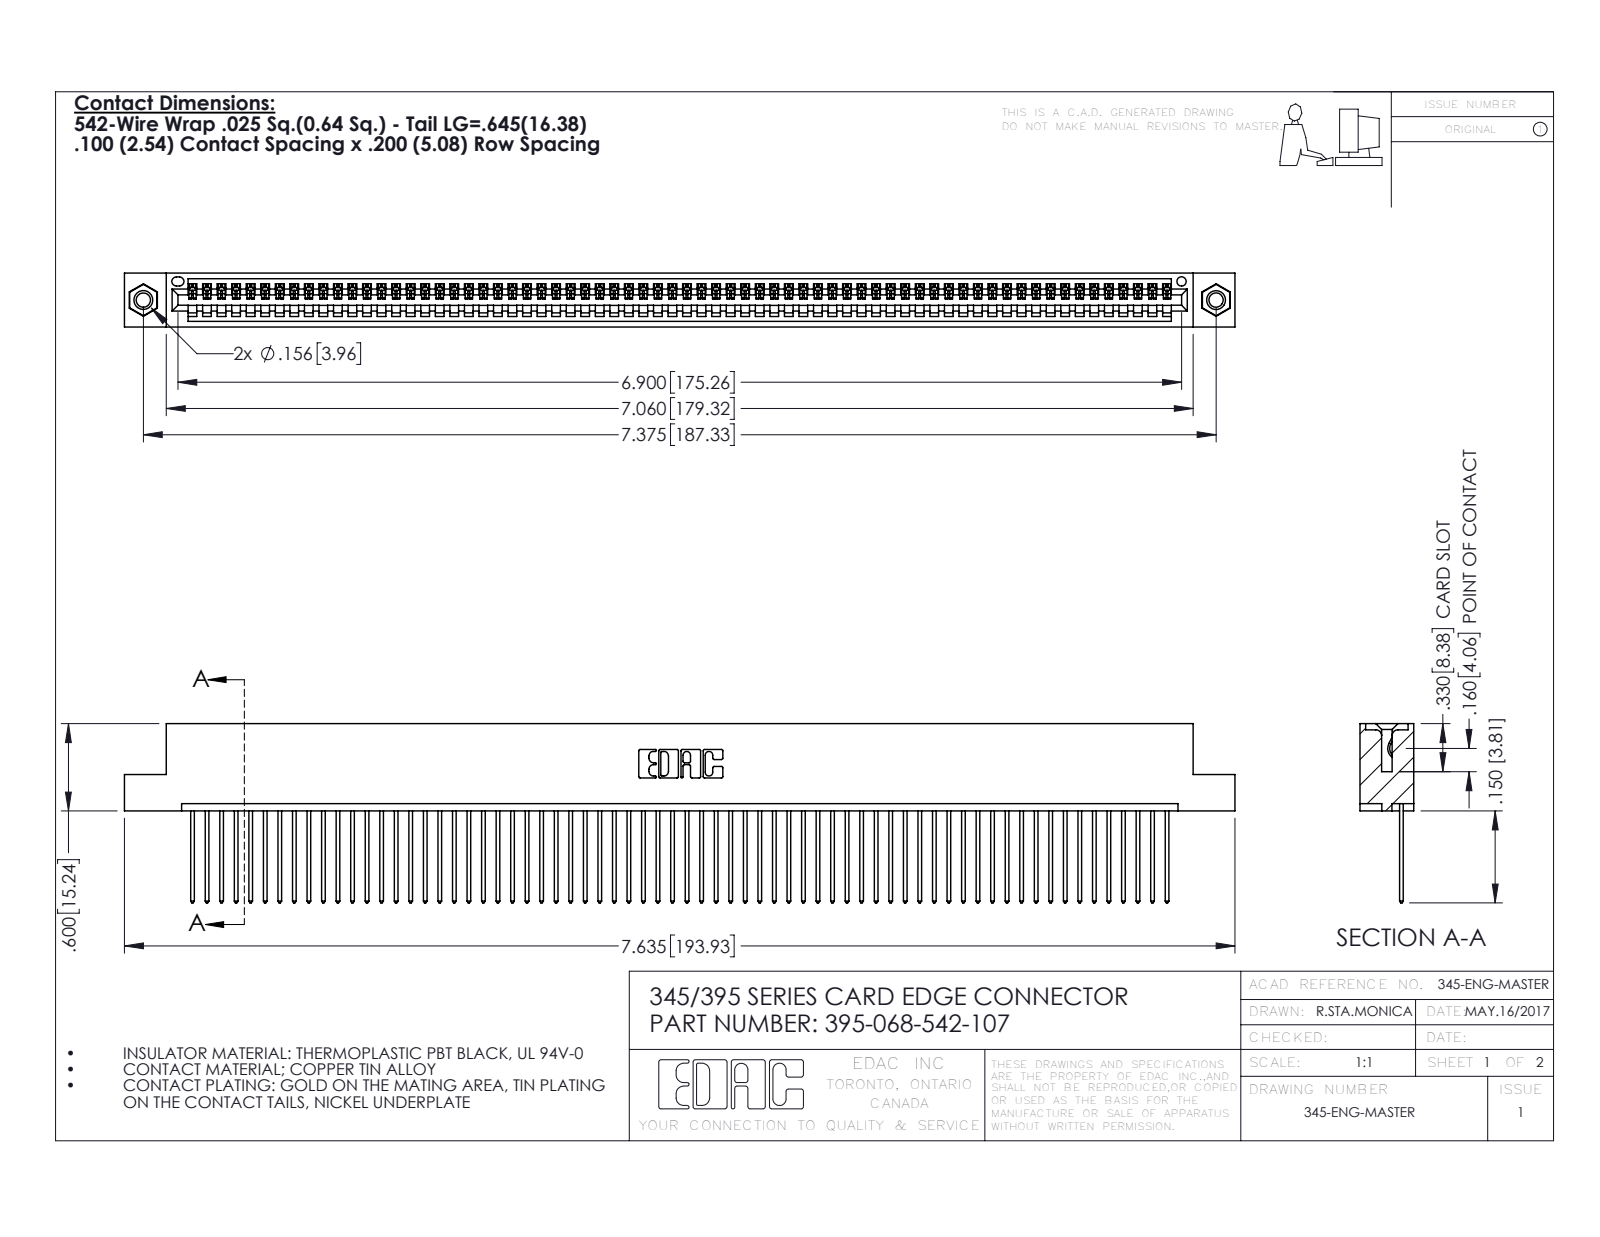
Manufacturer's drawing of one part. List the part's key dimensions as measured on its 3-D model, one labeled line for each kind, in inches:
Part name (STEP PRODUCT): 395-068-542-107; 345 Part_Flush Mounting Lugs - 0.156 Dia-TI; 345-292-001_345-293-142; 345-250-001_345-250-005-103
STEP written by: SolidWorks 2016 (CONFIG_CONTROL_DESIGN)
Units: inches
Bodies: 71 solids, 4130 faces (2832 planar, 1282 cylindrical, 16 other)
Overall size (bounding box): 7.635 × 1.232 × 0.37
Volume: 1.145 in³ · Surface area: 40.74 in²
Round holes (diameter × count): ⌀0.098 ×2, ⌀0.125 ×2, ⌀0.156 ×2, ⌀0.064 ×1
Round bosses / shafts (diameter × count): ⌀0.155 ×2
Partial cylindrical surfaces — rounded edges, fillets, slot ends (radius × count): R0.006 ×136, R0.01 ×136, R0.01 ×22, R0.007 ×6, R0.031 ×6, R0.026 ×3, R0.031 ×2, R0.04 ×2
Main face-to-face distances: 0.072, 0.298, 0.098, 0.272, 0.025, 0.37, 0.2, 0.225, 0.149, 0.072
Hole centre spacings: 0.27, 7.139, 7.375
